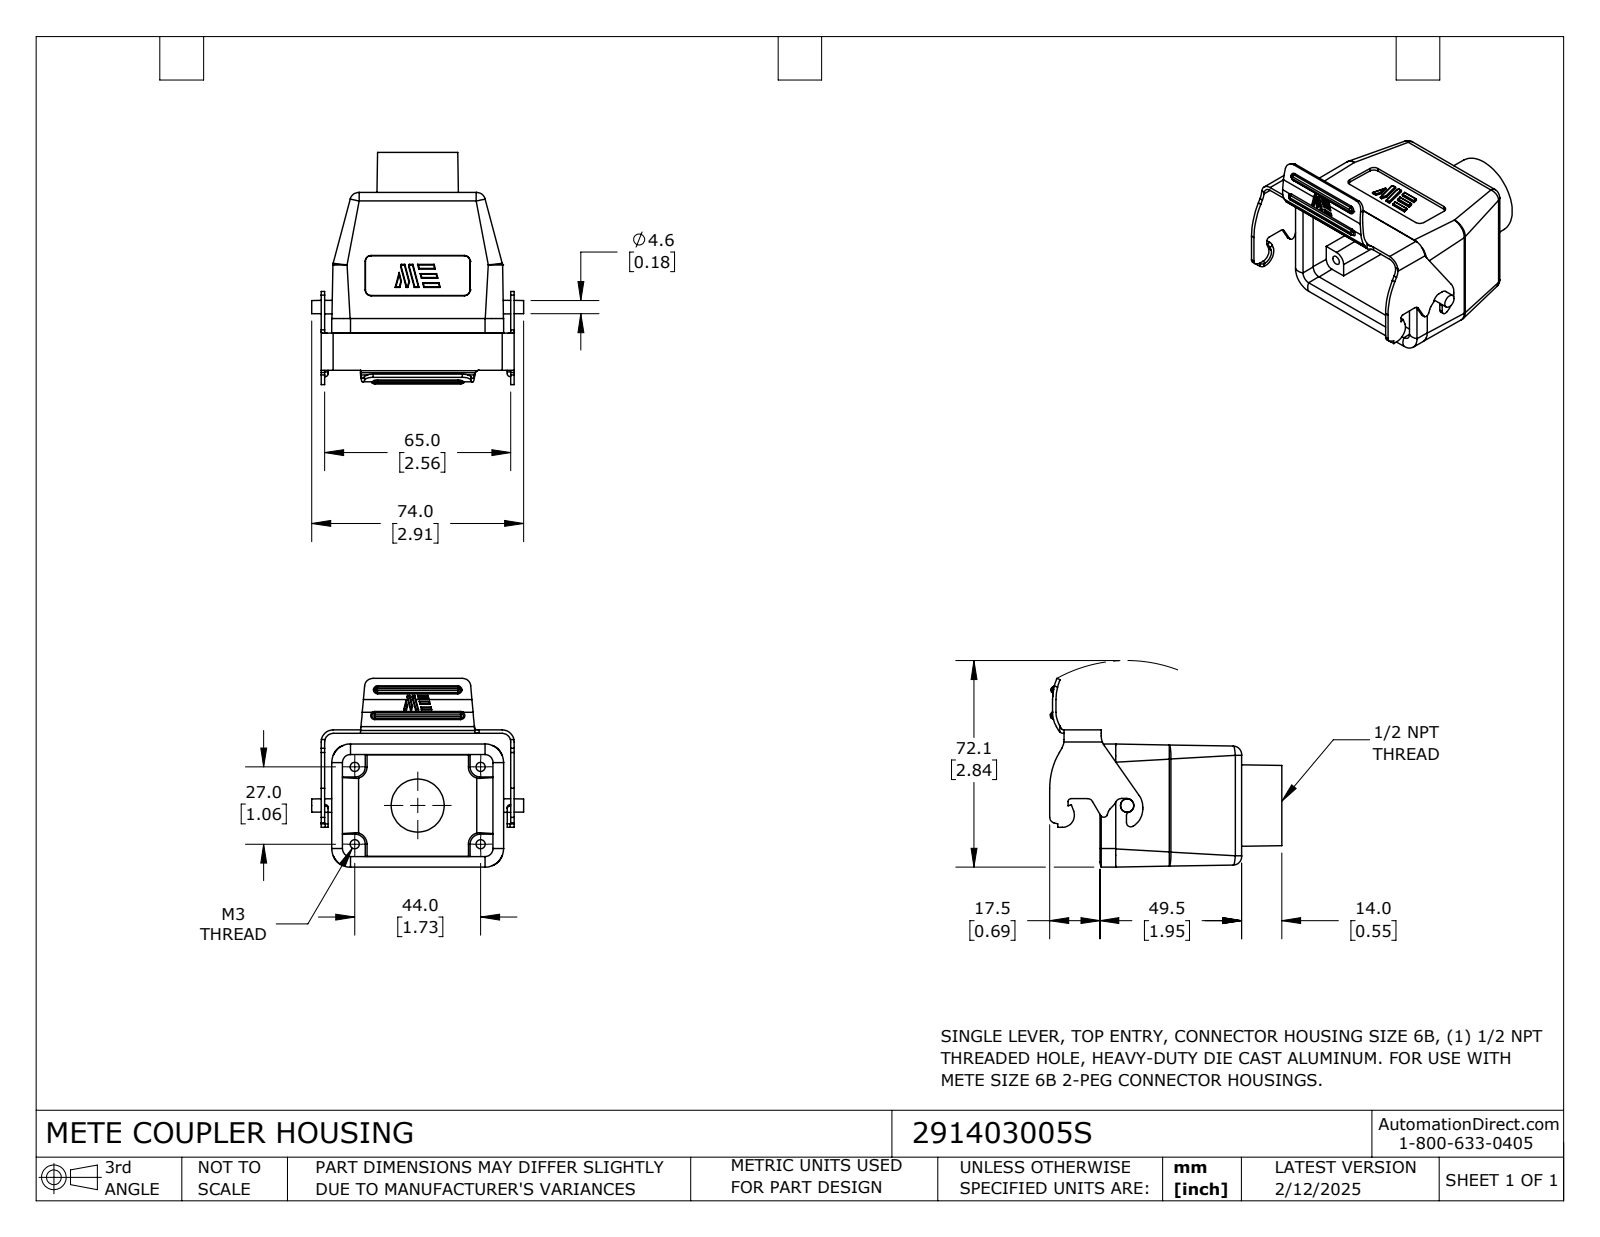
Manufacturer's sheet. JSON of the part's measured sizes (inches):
{"part_name": "291403005S", "step_written_by": "SolidWorks 2024 (CONFIG_CONTROL_DESIGN)", "units": "inches", "bodies": {"solids": 1, "faces": 479, "planar": 199, "cylindrical": 200, "other": 80}, "overall_size": [3.191, 2.913, 2.594], "volume_in3": 2.663, "surface_area_in2": 48.78, "round_holes": [[0.126, 4], [0.728, 1]], "partial_cylinders_radius": [[0.008, 56], [0.039, 12], [0.079, 11], [0.118, 9], [0.02, 5], [0.098, 5], [0.028, 4], [0.11, 4]], "face_to_face_distances": [0.118, 0.047, 0.146, 2.606, 0.041, 0.077, 2.559, 0.337, 0.455, 2.654], "hole_center_spacings": [1.016, 1.063, 1.732, 2.032]}
